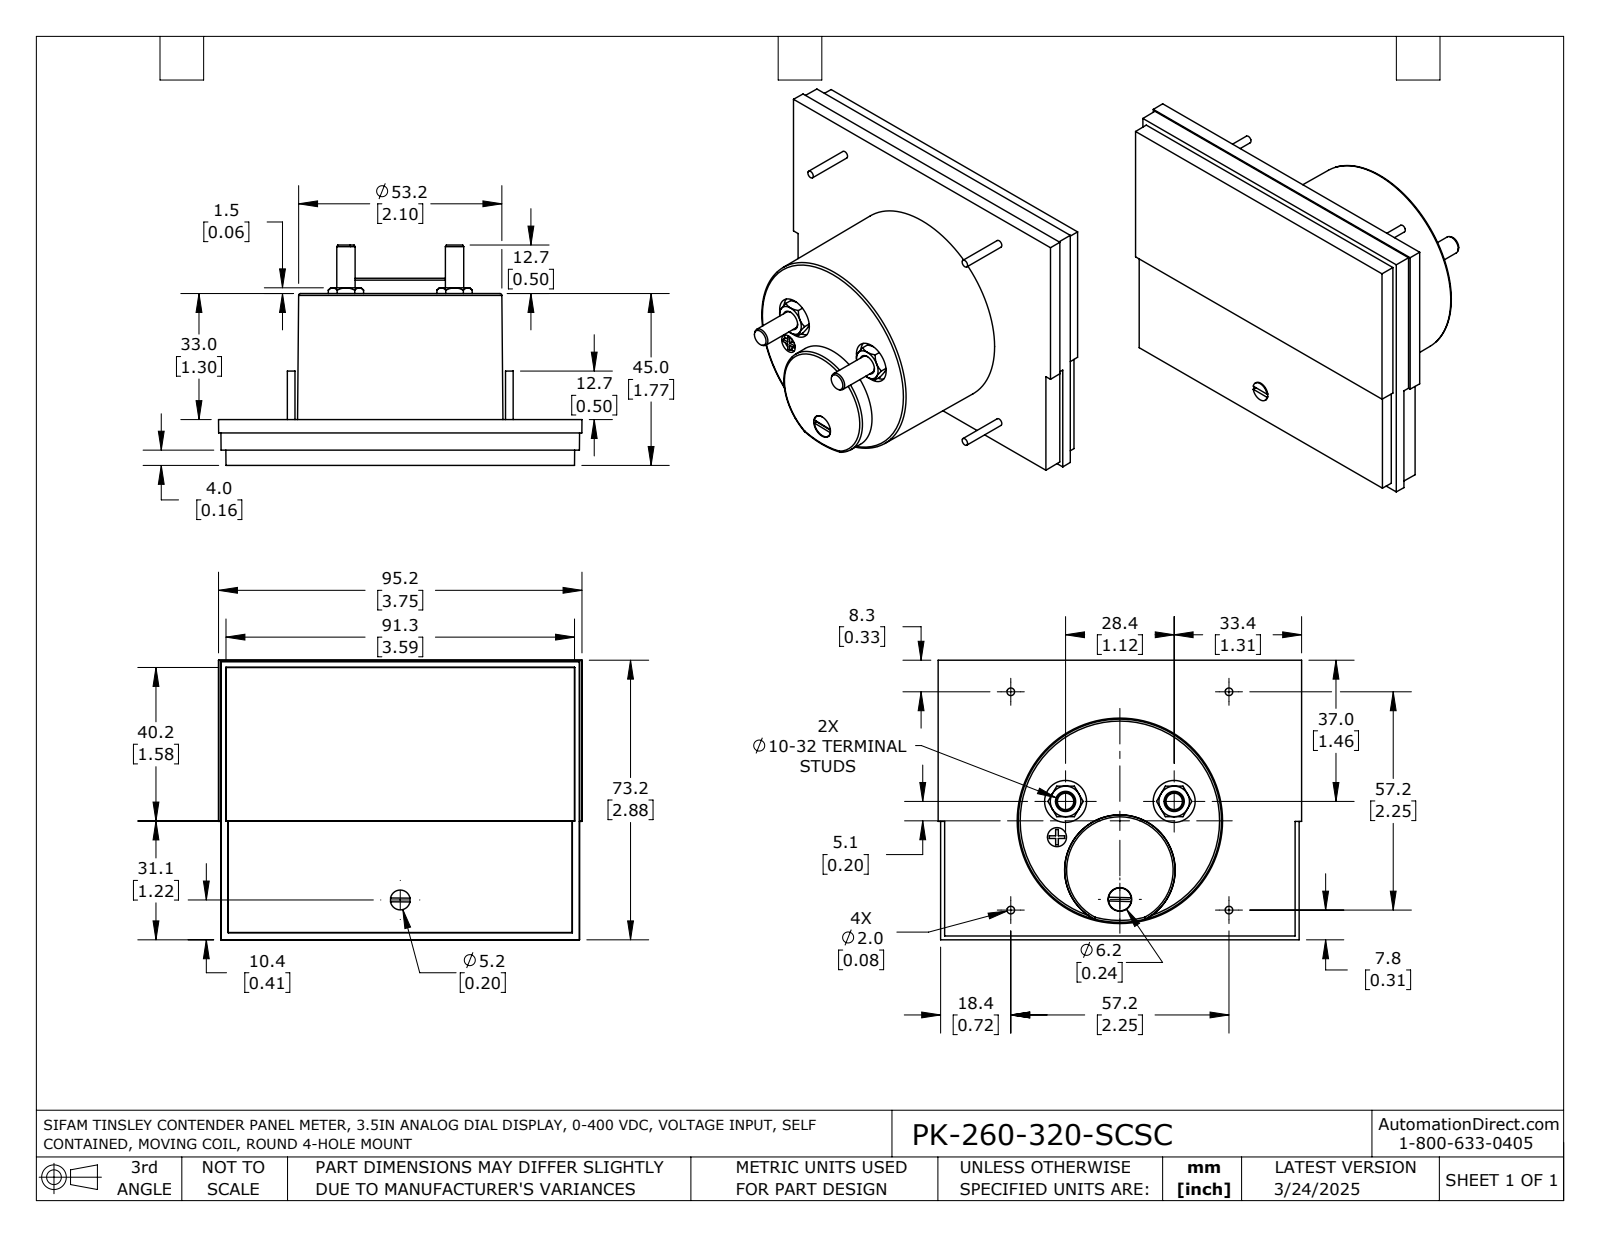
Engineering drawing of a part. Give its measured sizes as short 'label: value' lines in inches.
name: PK-260-320-SCSC
written by: SolidWorks 2021 (AUTOMOTIVE_DESIGN)
unit: in
bodies: 1 solid, 163 faces (76 planar, 31 cylindrical, 56 other)
size: 3.748 × 2.882 × 2.272
volume: 9.446 in³; area: 38.39 in²
holes: 2× ⌀0.433, 1× ⌀0.197, 1× ⌀0.244
bosses: 4× ⌀0.079, 2× ⌀0.189, 1× ⌀0.236, 1× ⌀0.205
rounds: 1× R0.1
face distances: 0.472, 0.03, 0.443, 1.772, 1.299, 1.742, 0.157, 0.073, 0.315, 1.457
hole spacings: 1.155, 0.379, 0.912, 1.12, 1.263
